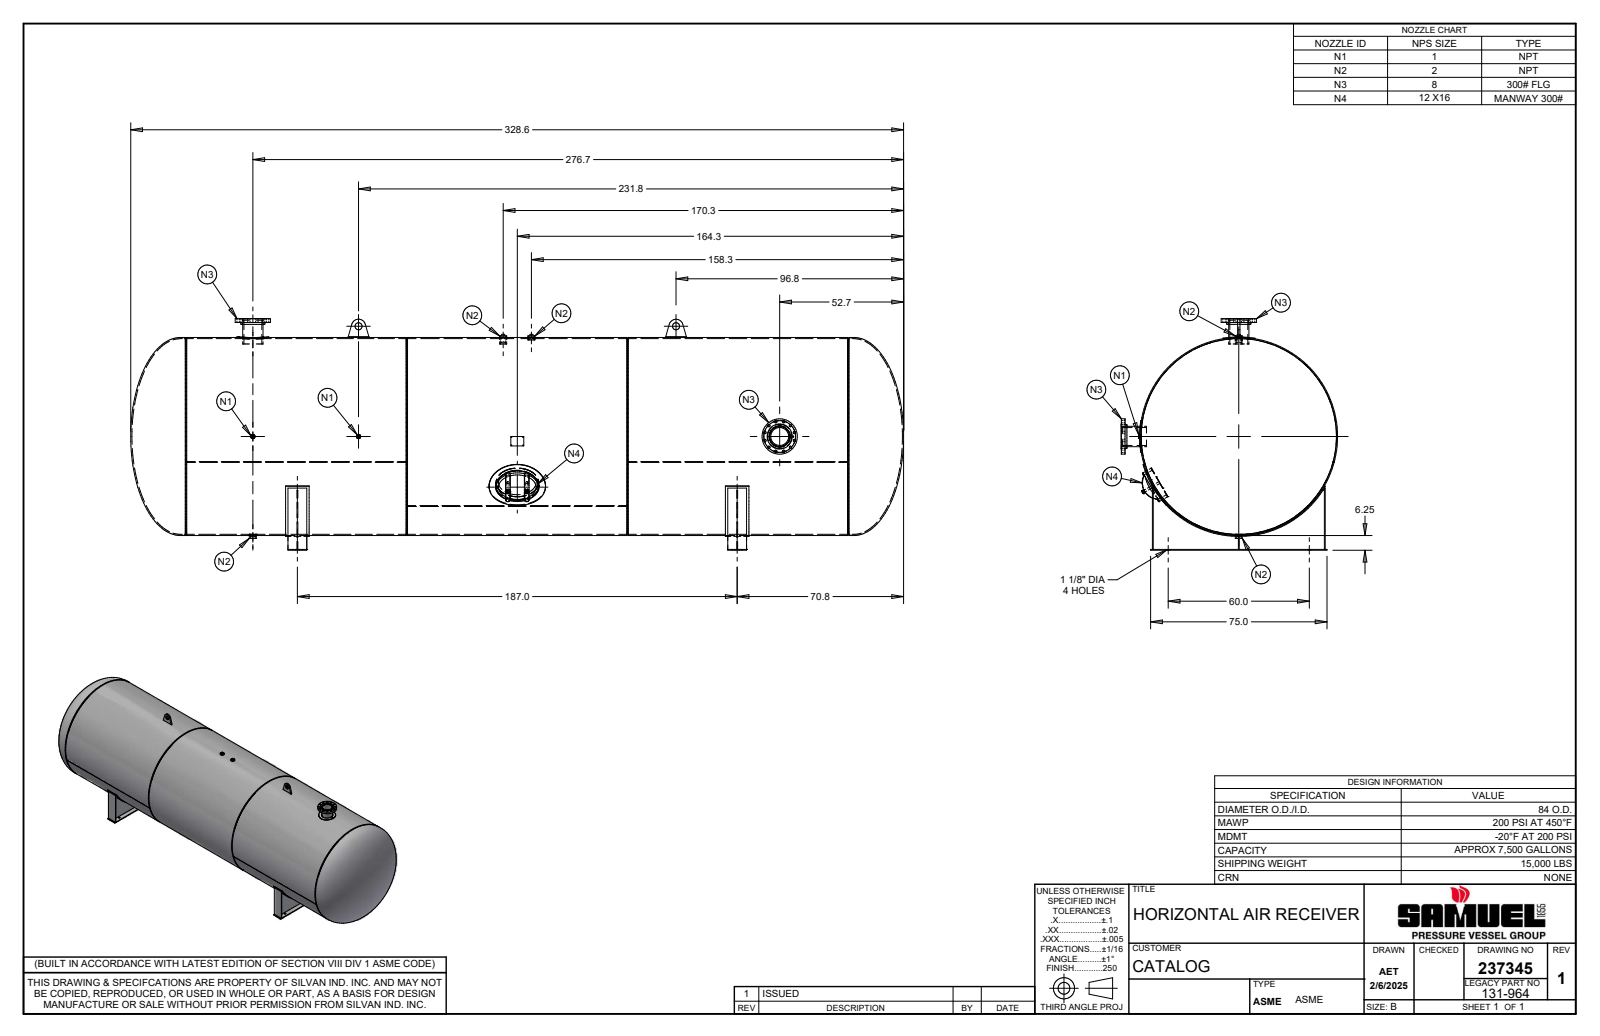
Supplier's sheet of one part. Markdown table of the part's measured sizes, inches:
| quantity | value |
| --- | --- |
| part name | 237345; 131-964-1; 131-964-2; 131-964-3 (+8 more) |
| STEP written by | Autodesk Inventor 2022 (AUTOMOTIVE_DESIGN) |
| units | inches |
| bodies | 40 solids, 424 faces (200 planar, 135 cylindrical, 89 other) |
| overall size | 328.625 × 98.25 × 92 |
| volume | 48 313 in³ |
| surface area | 197 117 in² |
| round holes (diameter × count) | 1 × 24, 1.125 × 10, 0.25 × 4, 2.172 × 3, 3.063 × 3, 0.906 × 2, 1.813 × 2, 3 × 2, 7.625 × 2, 8.72 × 2, 8.75 × 2, 83 × 1 |
| round bosses / shafts (diameter × count) | 3 × 3, 15 × 2, 10.625 × 2, 10.25 × 2, 8.625 × 2, 2.375 × 2, 1.75 × 2, 0.875 × 2 |
| partial cylindrical surfaces (radius × count) | 0.25 × 8, 0.5 × 6, 1 × 4, 3 × 2, 6.906 × 1, 7.031 × 1, 18.774 × 1, 42.125 × 1 |
| main face-to-face distances | 0.375, 187, 187.375, 186.625, 0.375, 73.125, 73.125, 72.75, 73.5, 36.563 |
| hole center spacings | 6.5, 3.365, 9.192, 11.258, 12.557, 13, 3, 60 |
